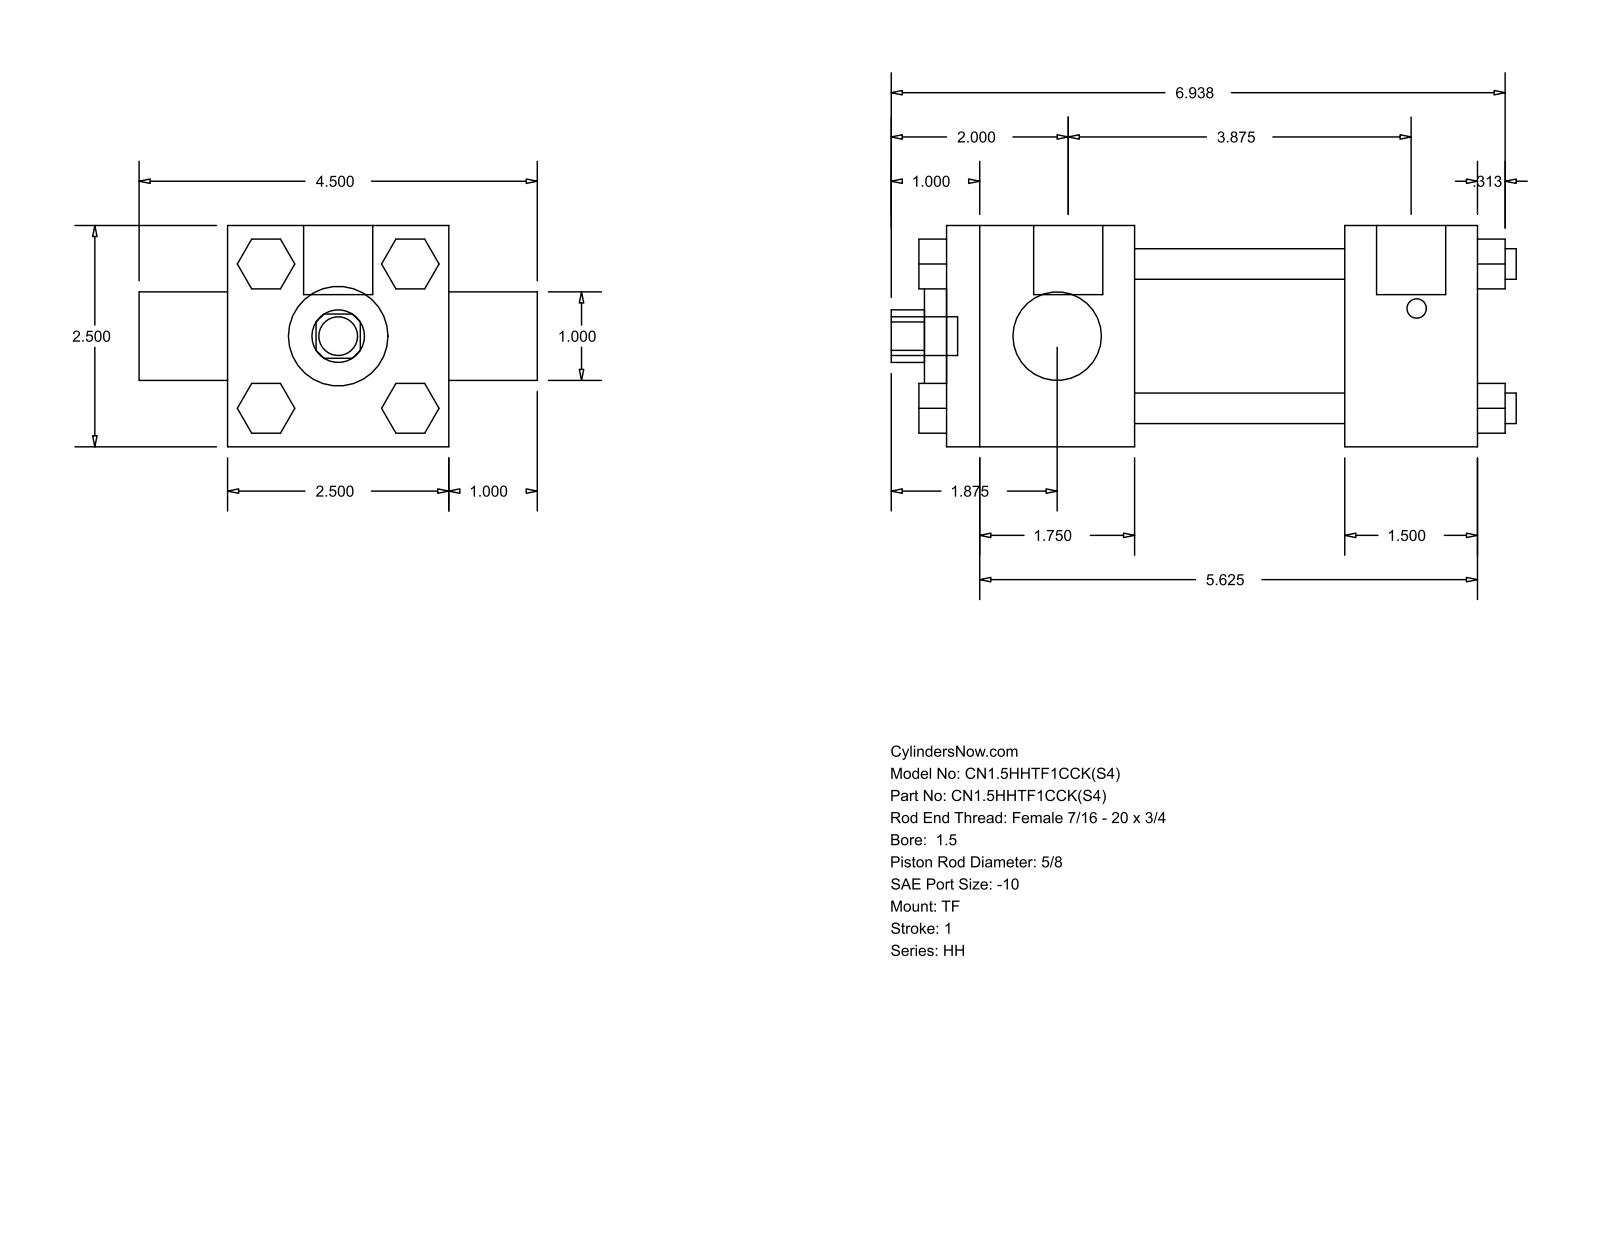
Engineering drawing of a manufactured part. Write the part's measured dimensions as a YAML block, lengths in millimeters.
part_name: "HH_TF__0150_0.625"
step_written_by: "GSSL Pune (CONFIG_CONTROL_DESIGN)"
units: millimeters
bodies: {solids: 0, faces: 120, planar: 92, cylindrical: 28, other: 0}
overall_size: [179.39, 114.3, 63.5]
round_holes:
  - {diameter: 15.88, count: 1}
  - {diameter: 25.4, count: 1}
  - {diameter: 28.57, count: 1}
  - {diameter: 44.45, count: 1}
round_bosses_or_shafts:
  - {diameter: 8.76, count: 4}
  - {diameter: 5.56, count: 3}
  - {diameter: 19.84, count: 2}
  - {diameter: 11.11, count: 1}
partial_cylinders:
  - {radius: 7.54, count: 1}
face_to_face_distances: [63.5, 114.3, 152.4, 38.1, 53.97, 98.43, 60.33, 25.4, 20.7, 14.29]
